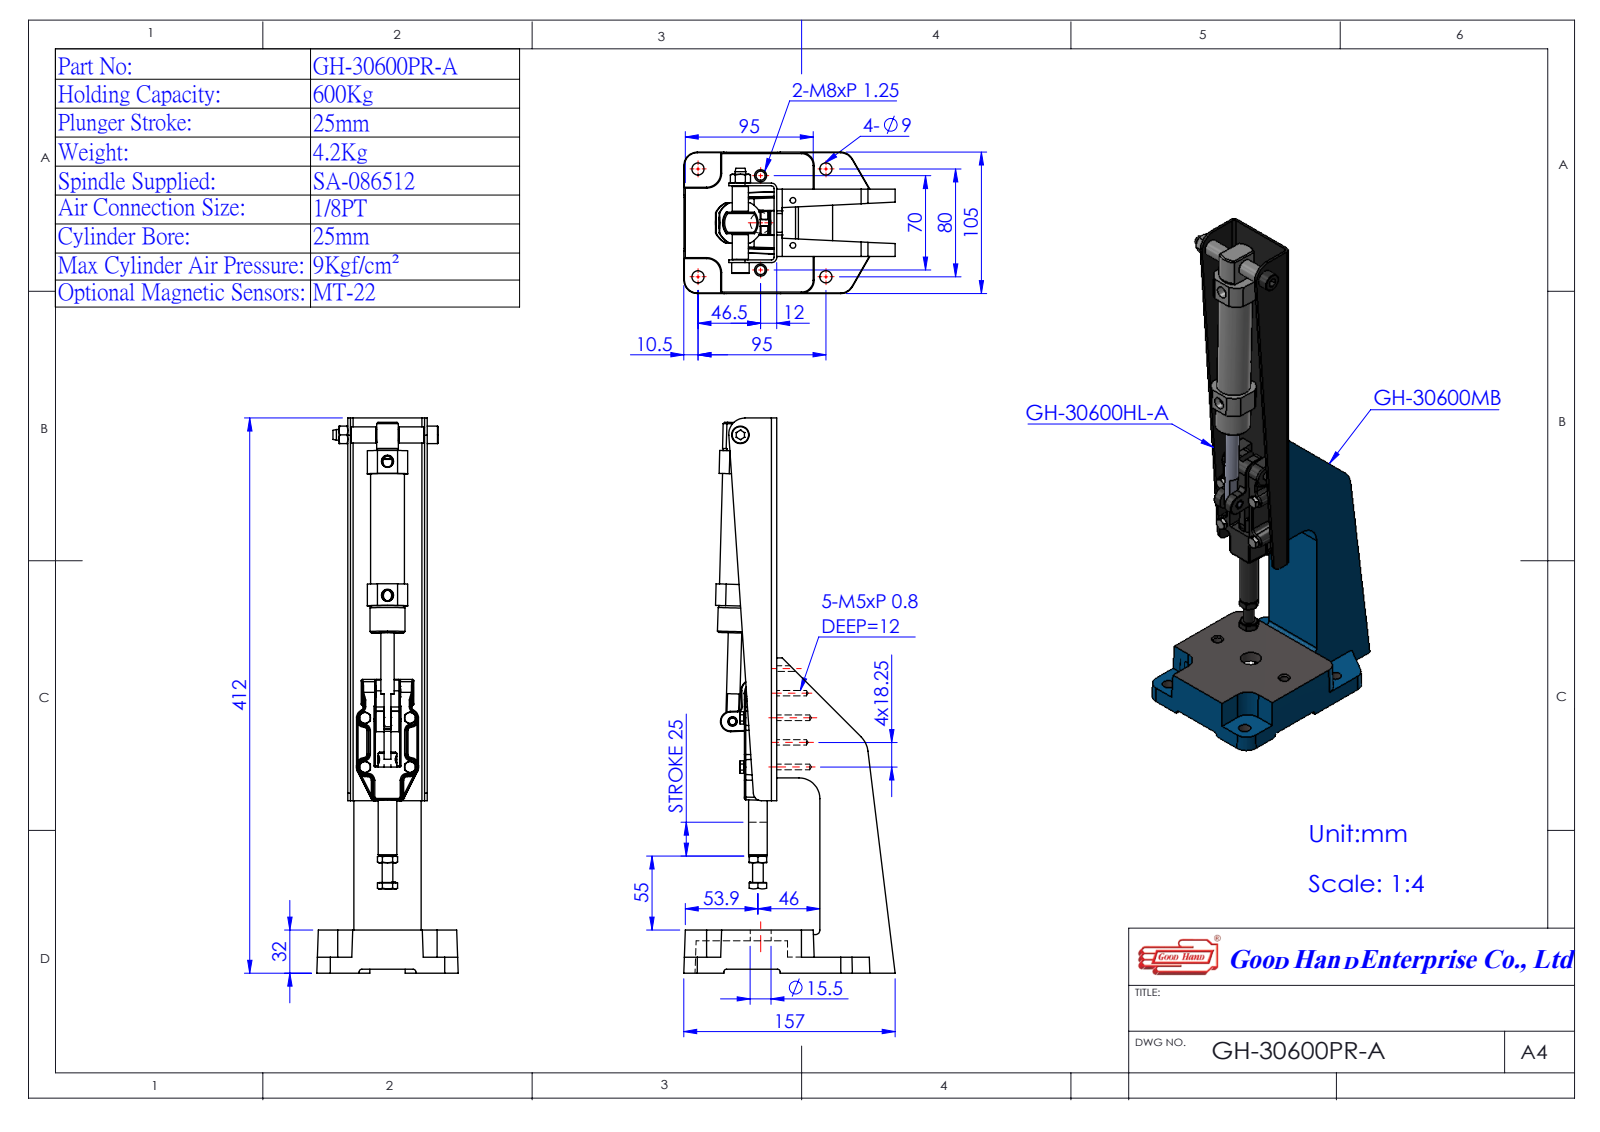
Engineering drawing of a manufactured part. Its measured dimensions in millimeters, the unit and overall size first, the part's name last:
Units: millimetres
Overall size (bounding box): 412 × 157 × 105
Round holes (diameter × count): ⌀4.2 ×6, ⌀4 ×4, ⌀9 ×4, ⌀5 ×3, ⌀6.8 ×3, ⌀6 ×2, ⌀7.9 ×2, ⌀10 ×1, ⌀12 ×1, ⌀13.95 ×1, ⌀15 ×1, ⌀15.5 ×1
Round bosses / shafts (diameter × count): ⌀8 ×5, ⌀5 ×4, ⌀25 ×2, ⌀13 ×2, ⌀26 ×1, ⌀14.97 ×1, ⌀10 ×1
Partial cylindrical surfaces — rounded edges, fillets, slot ends (radius × count): R1 ×35, R2 ×12, R7.5 ×3, R4 ×2, R5 ×2, R8 ×2, R10 ×2, R16.75 ×2
Main face-to-face distances: 2, 4.5, 2.5, 52.5, 54.5, 57, 32, 50, 24, 34
Hole centre spacings: 18.25, 38.06, 36.5, 49.48, 33.4, 54.75, 64.13, 35
Volume: 651 032 mm³ · Surface area: 226 308 mm²
Bodies: 8 solids, 885 faces (368 planar, 236 cylindrical, 281 other)
Part name (STEP PRODUCT): 零件32^GH-30600PR-A(簡化)-1; Group3^GH-30600PR-A(簡化)-1; Group4^GH-30600PR-A(簡化)-1; Group1^GH-30600PR-A(簡化)-1 (+5 more)
STEP written by: SolidWorks 2016 (AUTOMOTIVE_DESIGN)
